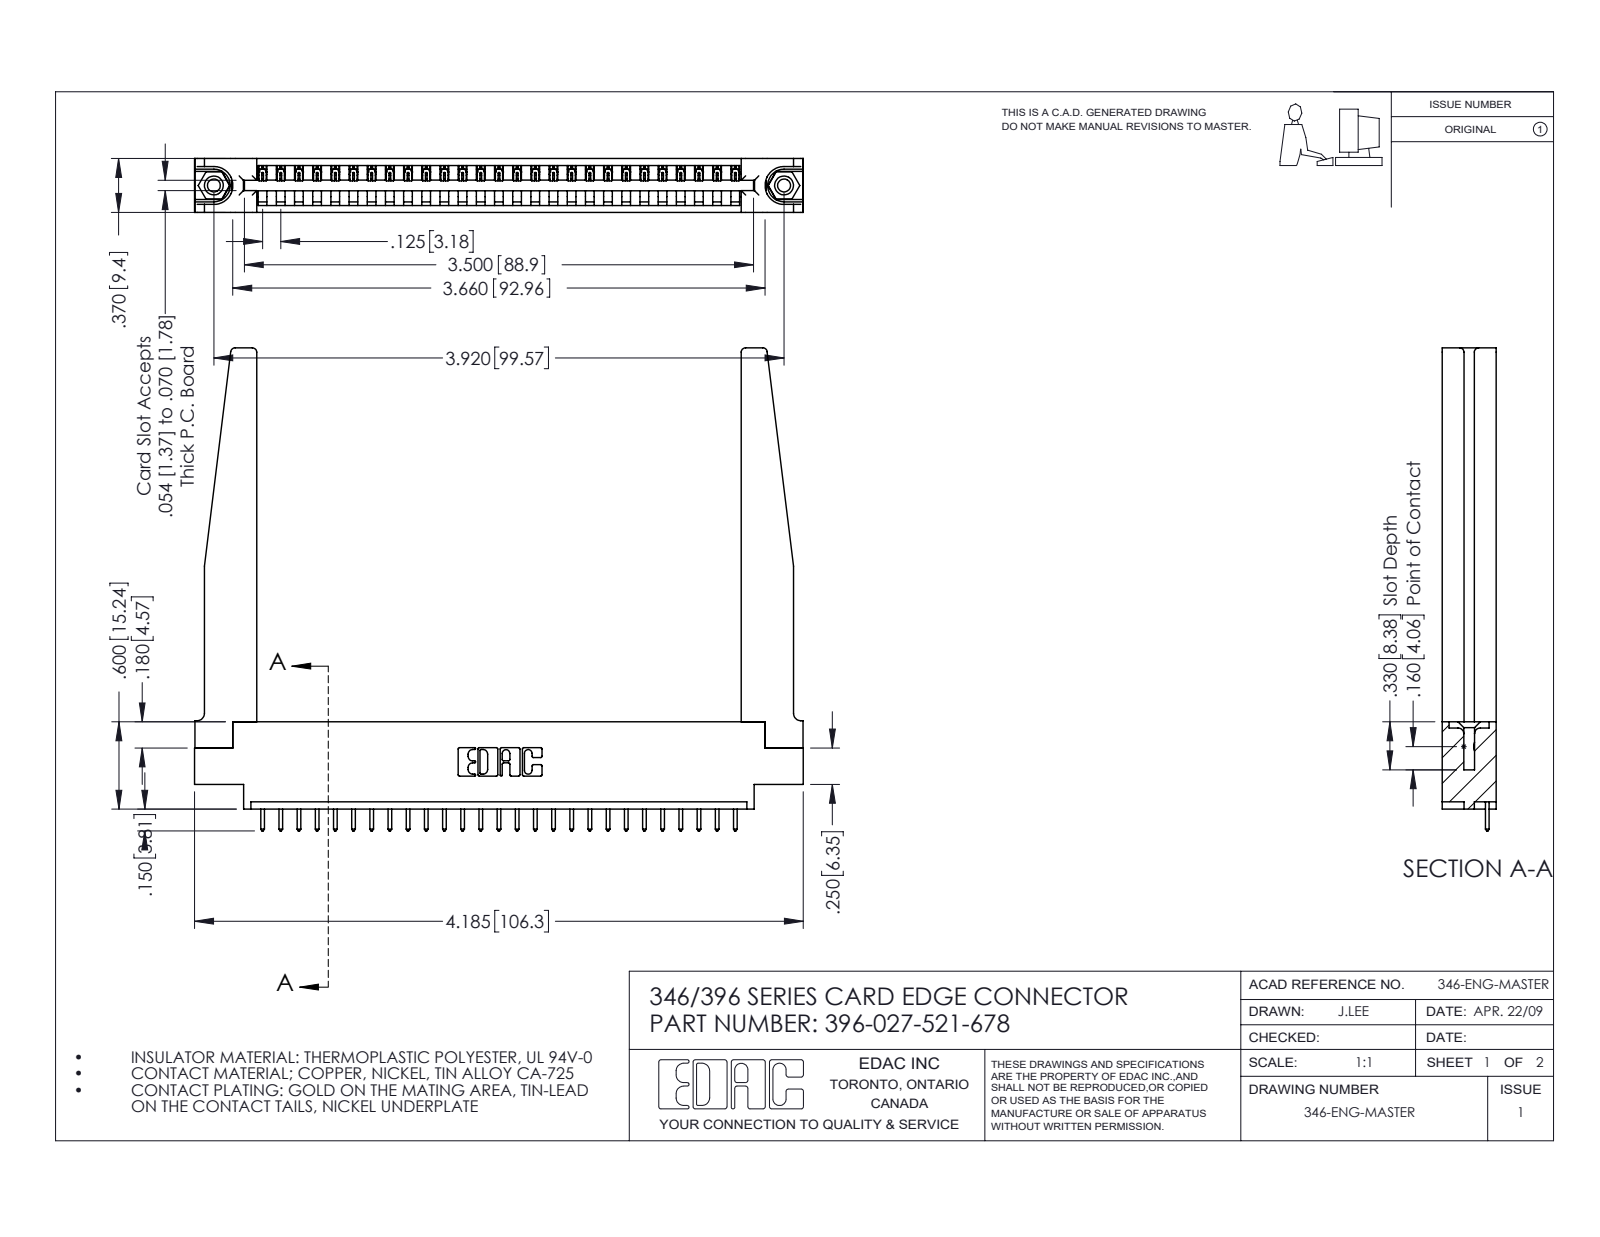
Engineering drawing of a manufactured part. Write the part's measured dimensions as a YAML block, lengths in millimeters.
part_name: "345-292-001_345-293-121; 346 Part_0.170 Offset - 0.156 Dia-TH; 396-027-521-678; 346-220-078_345-220-078 (+1 more)"
step_written_by: "SolidWorks 2016 (CONFIG_CONTROL_DESIGN)"
units: millimeters
bodies: {solids: 32, faces: 1926, planar: 1302, cylindrical: 572, other: 52}
overall_size: [106.3, 84.3, 9.4]
volume: 16750
surface_area: 18540
round_holes:
  - {diameter: 2.3, count: 2}
  - {diameter: 3.2, count: 2}
  - {diameter: 4, count: 2}
  - {diameter: 1.6, count: 1}
round_bosses_or_shafts:
  - {diameter: 3.9, count: 2}
partial_cylinders:
  - {radius: 0.2, count: 54}
  - {radius: 0.3, count: 54}
  - {radius: 0.3, count: 22}
  - {radius: 0.8, count: 8}
  - {radius: 0.2, count: 6}
  - {radius: 0.8, count: 6}
  - {radius: 0.7, count: 3}
  - {radius: 0.8, count: 2}
face_to_face_distances: [9.4, 1.2, 8.2, 1.8, 3.8, 3.8, 6.4, 7.6, 0.6, 5.6]
hole_center_spacings: [6.2, 94.3, 99.6]
